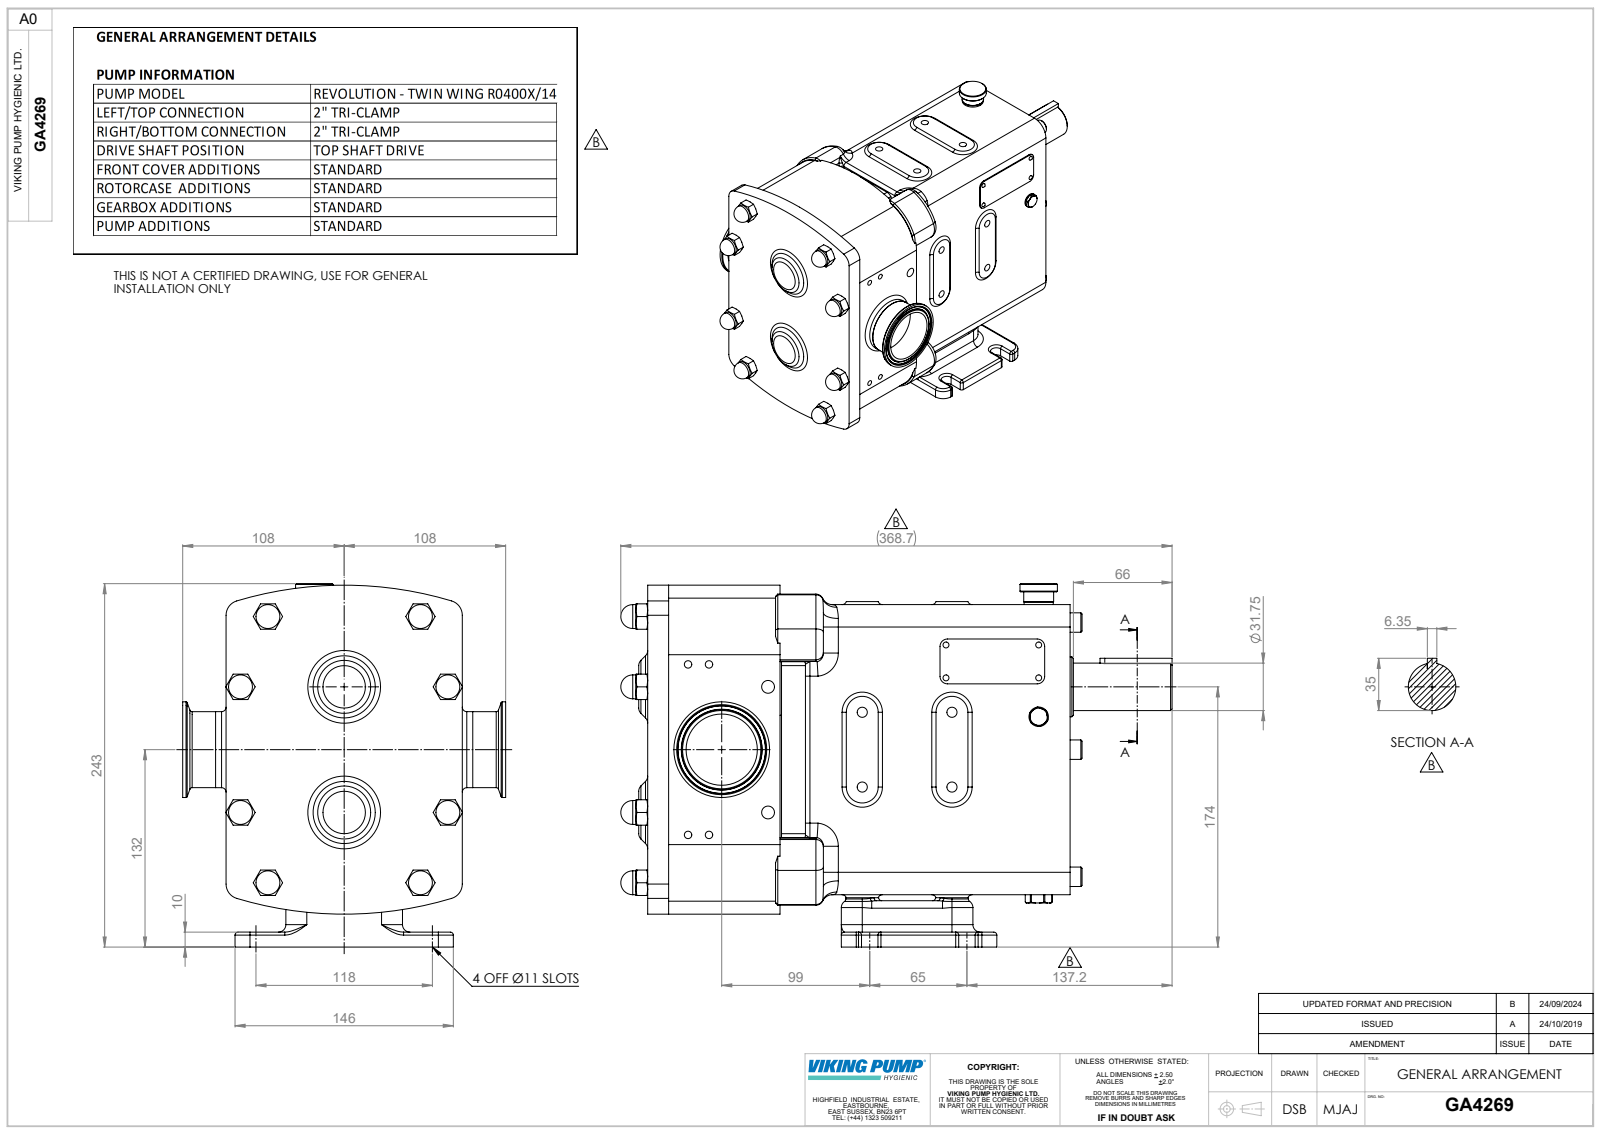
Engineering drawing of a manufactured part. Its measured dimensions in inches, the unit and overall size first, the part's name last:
Units: inches
Overall size (bounding box): 14.516 × 9.567 × 8.504
Round holes (diameter × count): ⌀0.268 ×8, ⌀0.197 ×4, ⌀0.339 ×2, ⌀0.906 ×1, ⌀1.876 ×1
Round bosses / shafts (diameter × count): ⌀0.63 ×8, ⌀0.512 ×7, ⌀2.52 ×1, ⌀2.002 ×1, ⌀2 ×1, ⌀1.575 ×1, ⌀1.496 ×1, ⌀1.25 ×1
Partial cylindrical surfaces — rounded edges, fillets, slot ends (radius × count): R0.394 ×30, R0.079 ×24, R0.118 ×20, R0.197 ×19, R0.232 ×8, R0.591 ×8, R0.217 ×4, R0.315 ×4
Main face-to-face distances: 7.638, 3.484, 0.945, 4.331, 11.122, 5.276, 3.524, 7.598, 0.039, 0.866
Hole centre spacings: 1.969, 2.362, 3.075, 0.551, 1.663, 2.055, 2.187, 2.269
Volume: 448.3 in³ · Surface area: 581 in²
Bodies: 3 solids, 917 faces (282 planar, 282 cylindrical, 353 other)
Part name (STEP PRODUCT): Copy of R0400 CPP H TSD^GA4269; GA4269; Copy of RA94-5121-33M^GA4269
STEP written by: SolidWorks 2023 (AUTOMOTIVE_DESIGN)
